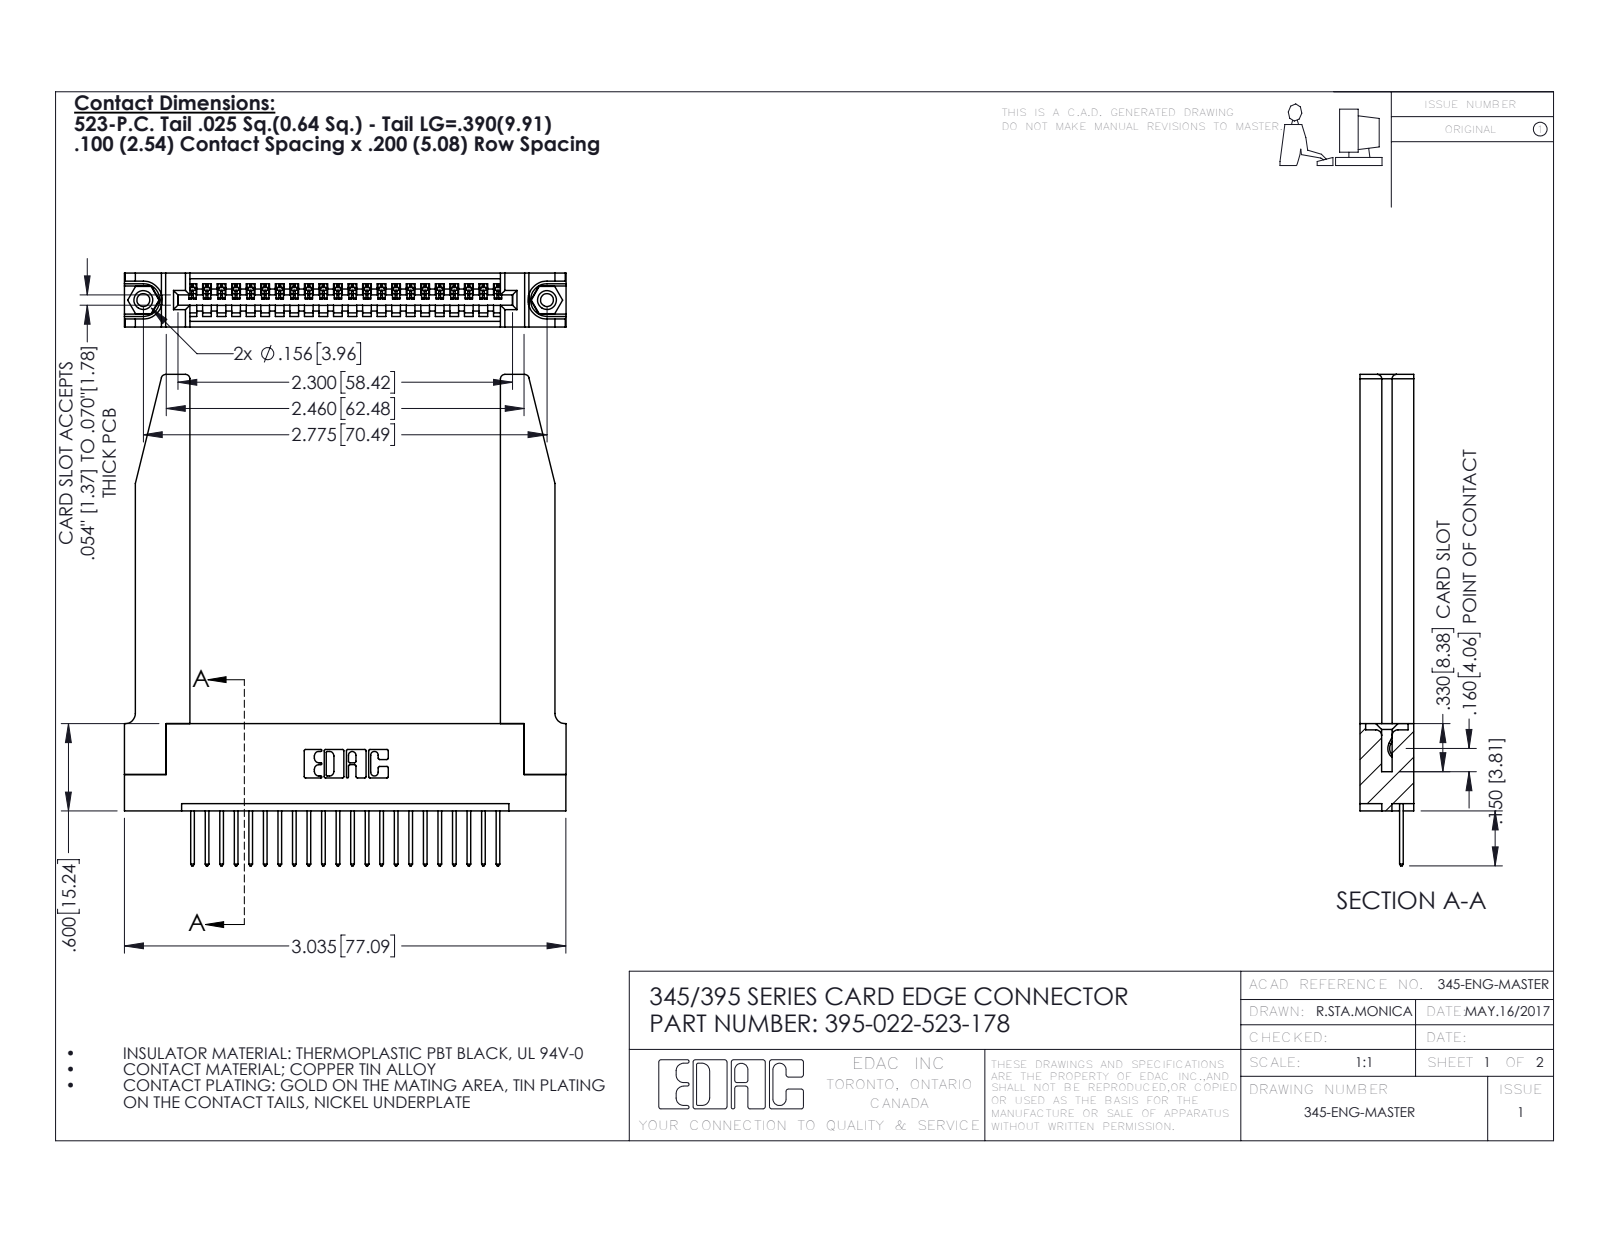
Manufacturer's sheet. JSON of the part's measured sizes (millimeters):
{"part_name": "345-220-078_345-220-078; 345-250-001_345-250-001-102; 345 Part_Flush Mounting Lugs - 0.156 Dia-TH; 395-022-523-178 (+1 more)", "step_written_by": "SolidWorks 2016 (CONFIG_CONTROL_DESIGN)", "units": "millimeters", "bodies": {"solids": 27, "faces": 1636, "planar": 1102, "cylindrical": 482, "other": 52}, "overall_size": [85.8, 77.1, 9.4], "volume_mm3": 14900, "surface_area_mm2": 16100, "round_holes": [[2.3, 2], [3.2, 2], [4, 2], [1.6, 1]], "round_bosses_or_shafts": [[3.9, 2]], "partial_cylinders_radius": [[0.2, 44], [0.3, 44], [0.3, 22], [0.8, 8], [0.2, 6], [0.8, 6], [0.7, 3], [0.8, 2]], "face_to_face_distances": [9.4, 1.8, 7.6, 5.1, 2.5, 6.9, 0.6, 3.8, 3.8, 2], "hole_center_spacings": [6.9, 64.5, 70.5]}
